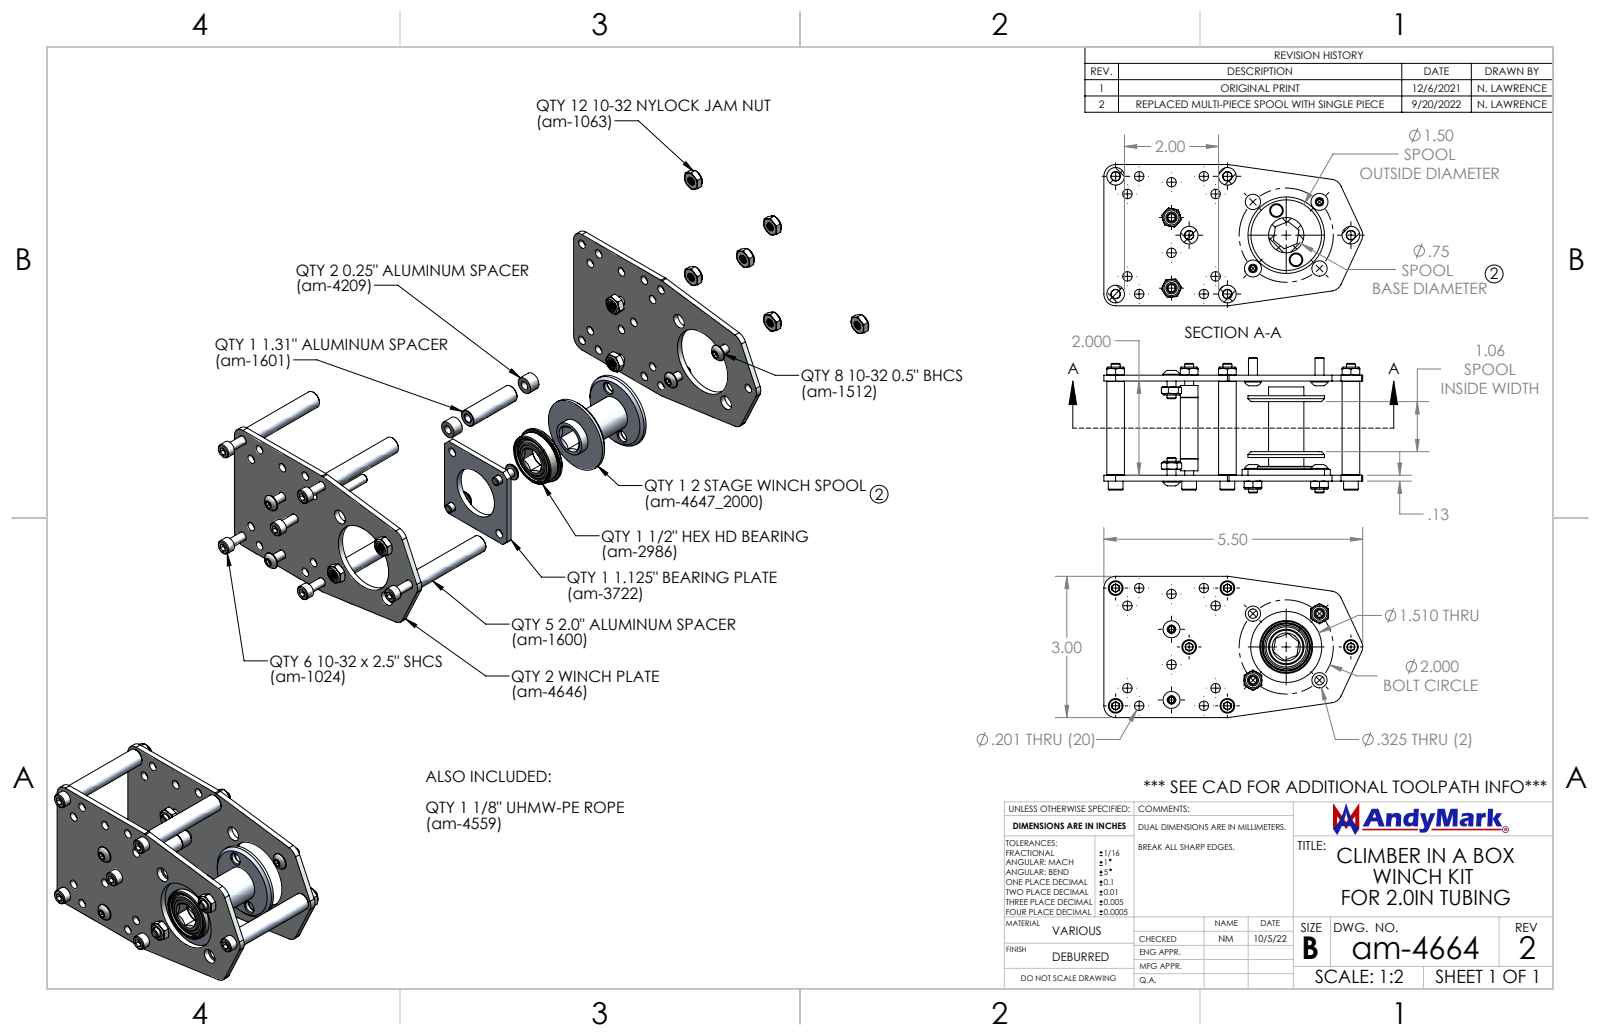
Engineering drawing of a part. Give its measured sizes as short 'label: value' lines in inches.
name: am-2986 FR8ZZ Hex Bearing; am-4647_2000 Full Winch Spool For 2 in. Box Tube; am-xxxx 1.313t x .192id x .375od AS38-10-84; 1.125 1.75in Bearing Plate (+7 more)
written by: SolidWorks 2022 (AUTOMOTIVE_DESIGN)
unit: in
bodies: 51 solids, 1145 faces (427 planar, 277 cylindrical, 441 other)
size: 5.5 × 3 × 2.875
volume: 6.092 in³; area: 129.9 in²
holes: 48× ⌀0.164, 22× ⌀0.201, 10× ⌀0.161, 10× ⌀0.19, 10× ⌀0.239, 2× ⌀0.25, 2× ⌀0.325, 1× ⌀0.192, 1× ⌀1.025, 1× ⌀1.125, 1× ⌀1.51
bosses: 6× ⌀0.375, 6× ⌀0.313, 4× ⌀0.361, 1× ⌀1.625, 1× ⌀1.625, 1× ⌀1.225, 1× ⌀1.125, 1× ⌀1.11
rounds: 12× R0.082, 7× R0.25
face distances: 0.125, 2.125, 2.25, 2, 0.125, 2, 1.875, 0.25, 0.376, 0.437
hole spacings: 2.375, 3.437, 0.015, 1.991, 4.335, 1.477, 1.988, 2.139
